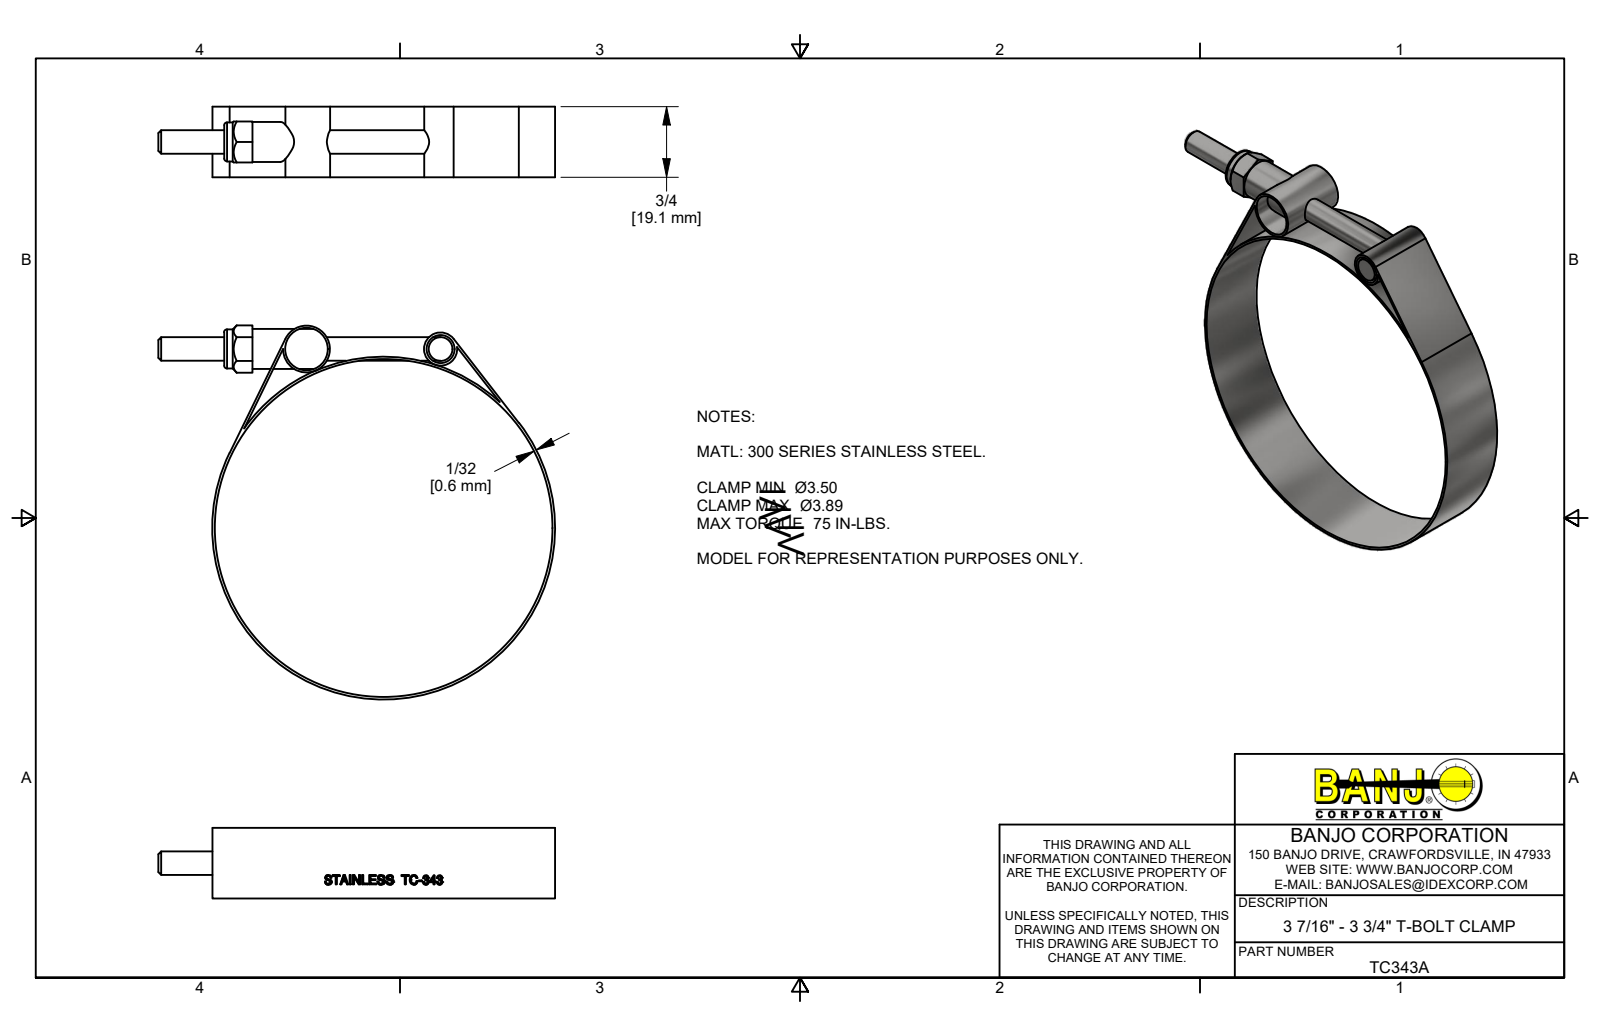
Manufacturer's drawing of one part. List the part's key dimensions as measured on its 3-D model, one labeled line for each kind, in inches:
Part name (STEP PRODUCT): TC343A
STEP written by: Autodesk Inventor 2019 (AUTOMOTIVE_DESIGN)
Units: inches
Bodies: 1 solid, 235 faces (100 planar, 37 cylindrical, 98 other)
Overall size (bounding box): 4.214 × 3.972 × 0.75
Volume: 0.565 in³ · Surface area: 26.56 in²
Round holes (diameter × count): ⌀0.3 ×1, ⌀0.45 ×1, ⌀3.59 ×1
Round bosses / shafts (diameter × count): ⌀0.25 ×2, ⌀3.64 ×1, ⌀0.5 ×1, ⌀0.425 ×1, ⌀0.415 ×1, ⌀0.35 ×1
Partial cylindrical surfaces — rounded edges, fillets, slot ends (radius × count): R1.815 ×1
Main face-to-face distances: 0.026, 0.025, 0.75, 0.157, 0.592, 0.435, 0.435, 0.7, 1, 0.3
Hole centre spacings: 1.425, 1.995, 2.07
